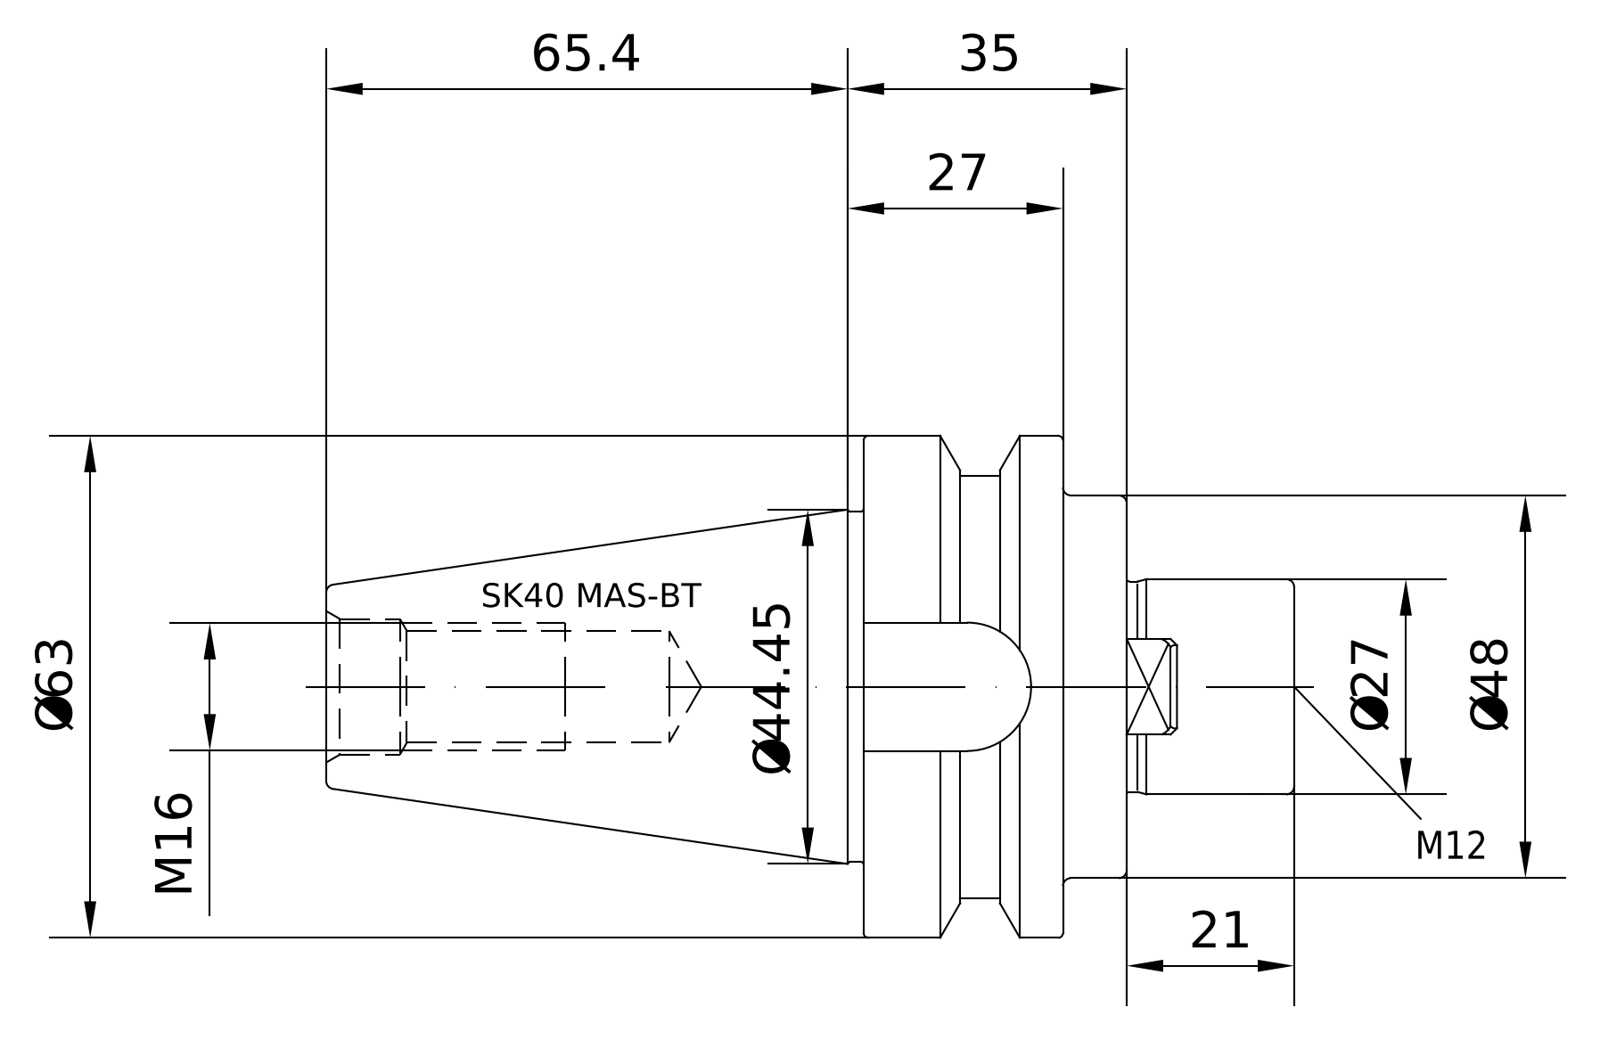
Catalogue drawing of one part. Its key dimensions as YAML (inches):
part_name: "40-550-27"
step_written_by: "PRO/ENGINEER BY PARAMETRIC TECHNOLOGY CORPORATION, 2010430 (CONFIG_CONTROL_DESIGN)"
units: inches
bodies: {solids: 1, faces: 119, planar: 43, cylindrical: 26, other: 50}
overall_size: [4.78, 2.48, 2.48]
volume: 9.218
surface_area: 42.3
round_holes:
  - {diameter: 0.402, count: 1}
  - {diameter: 0.472, count: 1}
  - {diameter: 0.545, count: 1}
  - {diameter: 0.67, count: 1}
  - {diameter: 0.689, count: 1}
round_bosses_or_shafts:
  - {diameter: 2.48, count: 1}
  - {diameter: 2.077, count: 1}
  - {diameter: 1.89, count: 1}
  - {diameter: 1.722, count: 1}
  - {diameter: 1.063, count: 1}
  - {diameter: 0.63, count: 1}
partial_cylinders:
  - {radius: 0.319, count: 1}
face_to_face_distances: [0.984, 1.299, 0.315, 2.126, 1.142, 0.827, 1.768, 0.083, 0.555, 1.547]
